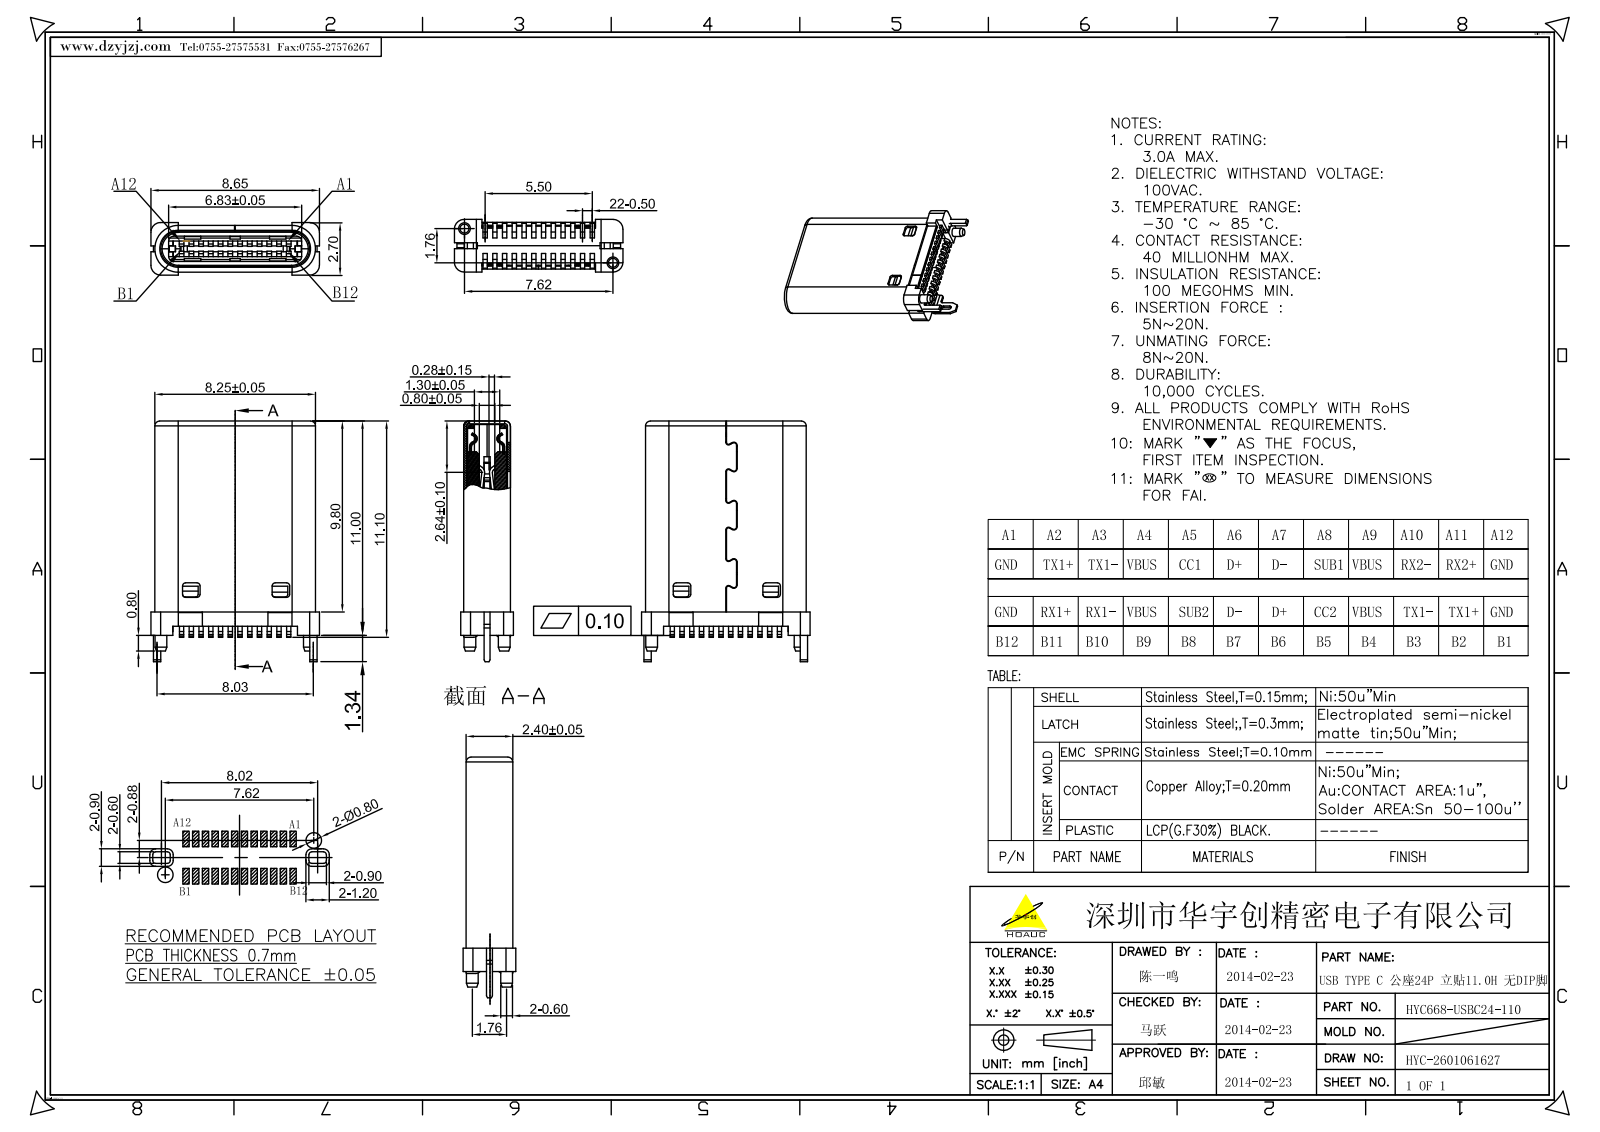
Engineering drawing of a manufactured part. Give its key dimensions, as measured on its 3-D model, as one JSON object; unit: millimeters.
{"part_name": "XDS-B_TC_2_F_105A", "step_written_by": "CREO PARAMETRIC BY PTC INC, 2025010 (AUTOMOTIVE_DESIGN)", "units": "millimeters", "bodies": {"solids": 1, "faces": 810, "planar": 594, "cylindrical": 208, "other": 8}, "overall_size": [12.34, 8.65, 2.7], "volume_mm3": 165, "surface_area_mm2": 427, "round_bosses_or_shafts": [[0.6, 2]], "partial_cylinders_radius": [[0.15, 24], [0.13, 16], [0.13, 12], [0.25, 8], [0.1, 6], [0.1, 6], [0.16, 6], [0.16, 4]], "face_to_face_distances": [0.8, 2.4, 1.6, 1.05, 0.55, 0.5, 1.85, 1.3, 1.2, 2]}
